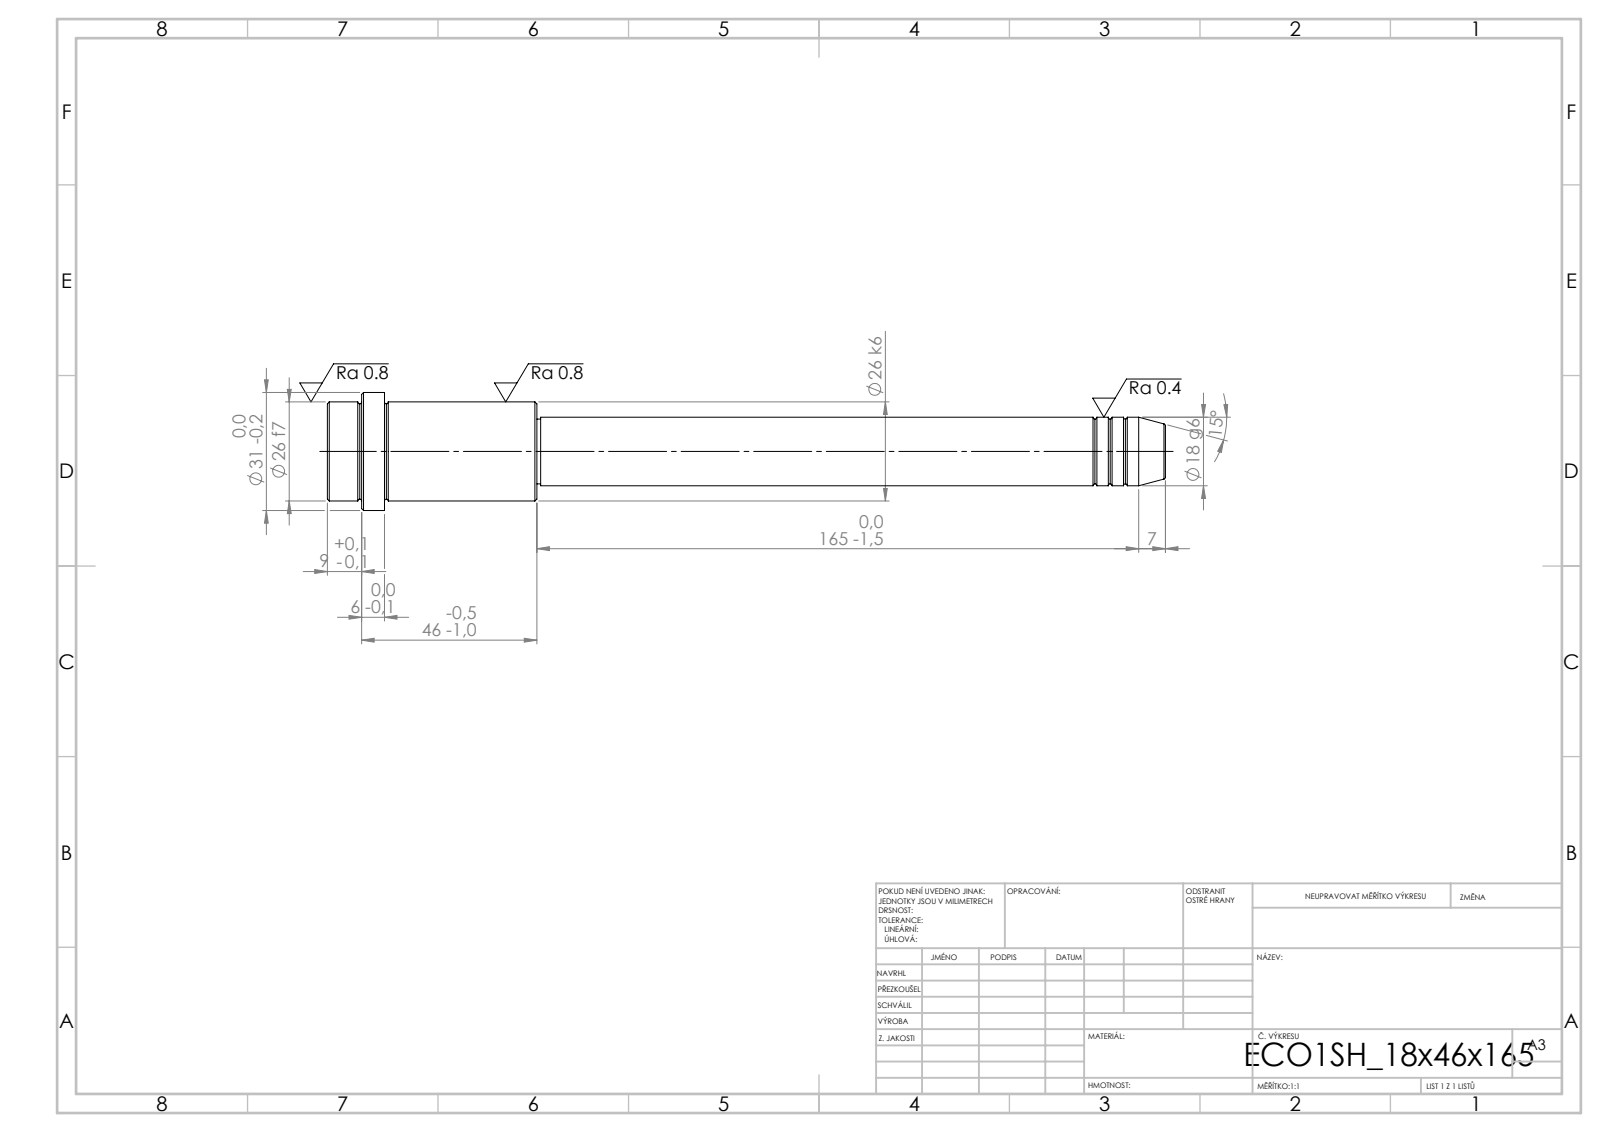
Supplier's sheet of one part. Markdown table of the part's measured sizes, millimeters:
| quantity | value |
| --- | --- |
| STEP written by | SolidWorks 2019 (CONFIG_CONTROL_DESIGN) |
| units | millimeters |
| bodies | 1 solid, 52 faces (6 planar, 16 cylindrical, 30 other) |
| overall size | 220 × 31 × 31 |
| volume | 71 997 mm³ |
| surface area | 15 447 mm² |
| round bosses / shafts (diameter × count) | 31 × 1, 26 × 1, 18 × 1, 17 × 1 |
| main face-to-face distances | 55, 40, 15, 46, 6, 9, 165, 205, 211, 220 |
